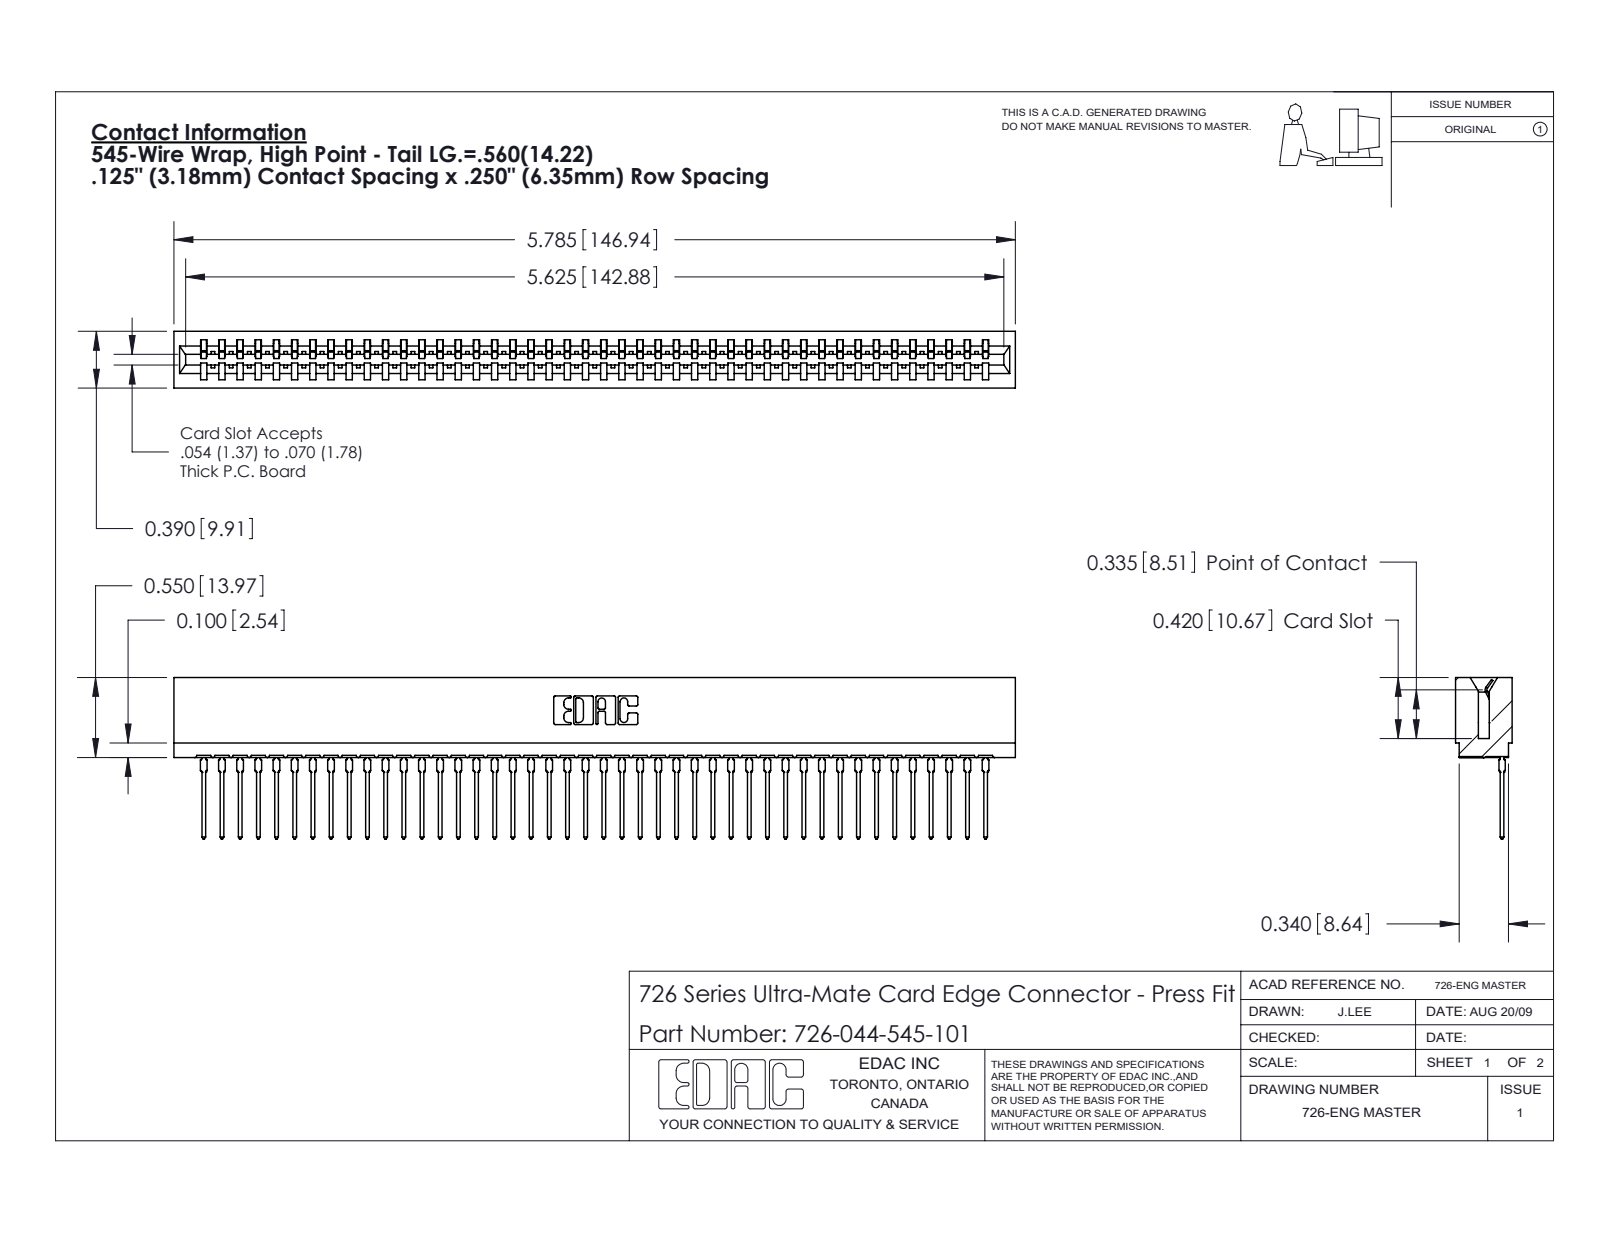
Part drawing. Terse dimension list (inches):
name: 746-292-001_545; 726 Part_.515 Slot Depth - 01; 726-044-545-101
written by: SolidWorks 2020 (CONFIG_CONTROL_DESIGN)
unit: in
bodies: 45 solids, 4849 faces (2827 planar, 878 cylindrical, 1144 other)
size: 5.785 × 1.109 × 0.39
volume: 0.807 in³; area: 32.3 in²
rounds: 88× R0.021, 45× R0.015, 22× R0.01, 6× R0.007, 6× R0.031, 4× R0.005, 4× R0.011, 3× R0.026
face distances: 0.057, 0.333, 0.39, 0.025, 0.307, 0.25, 0.083, 0.275, 0.365, 0.032
